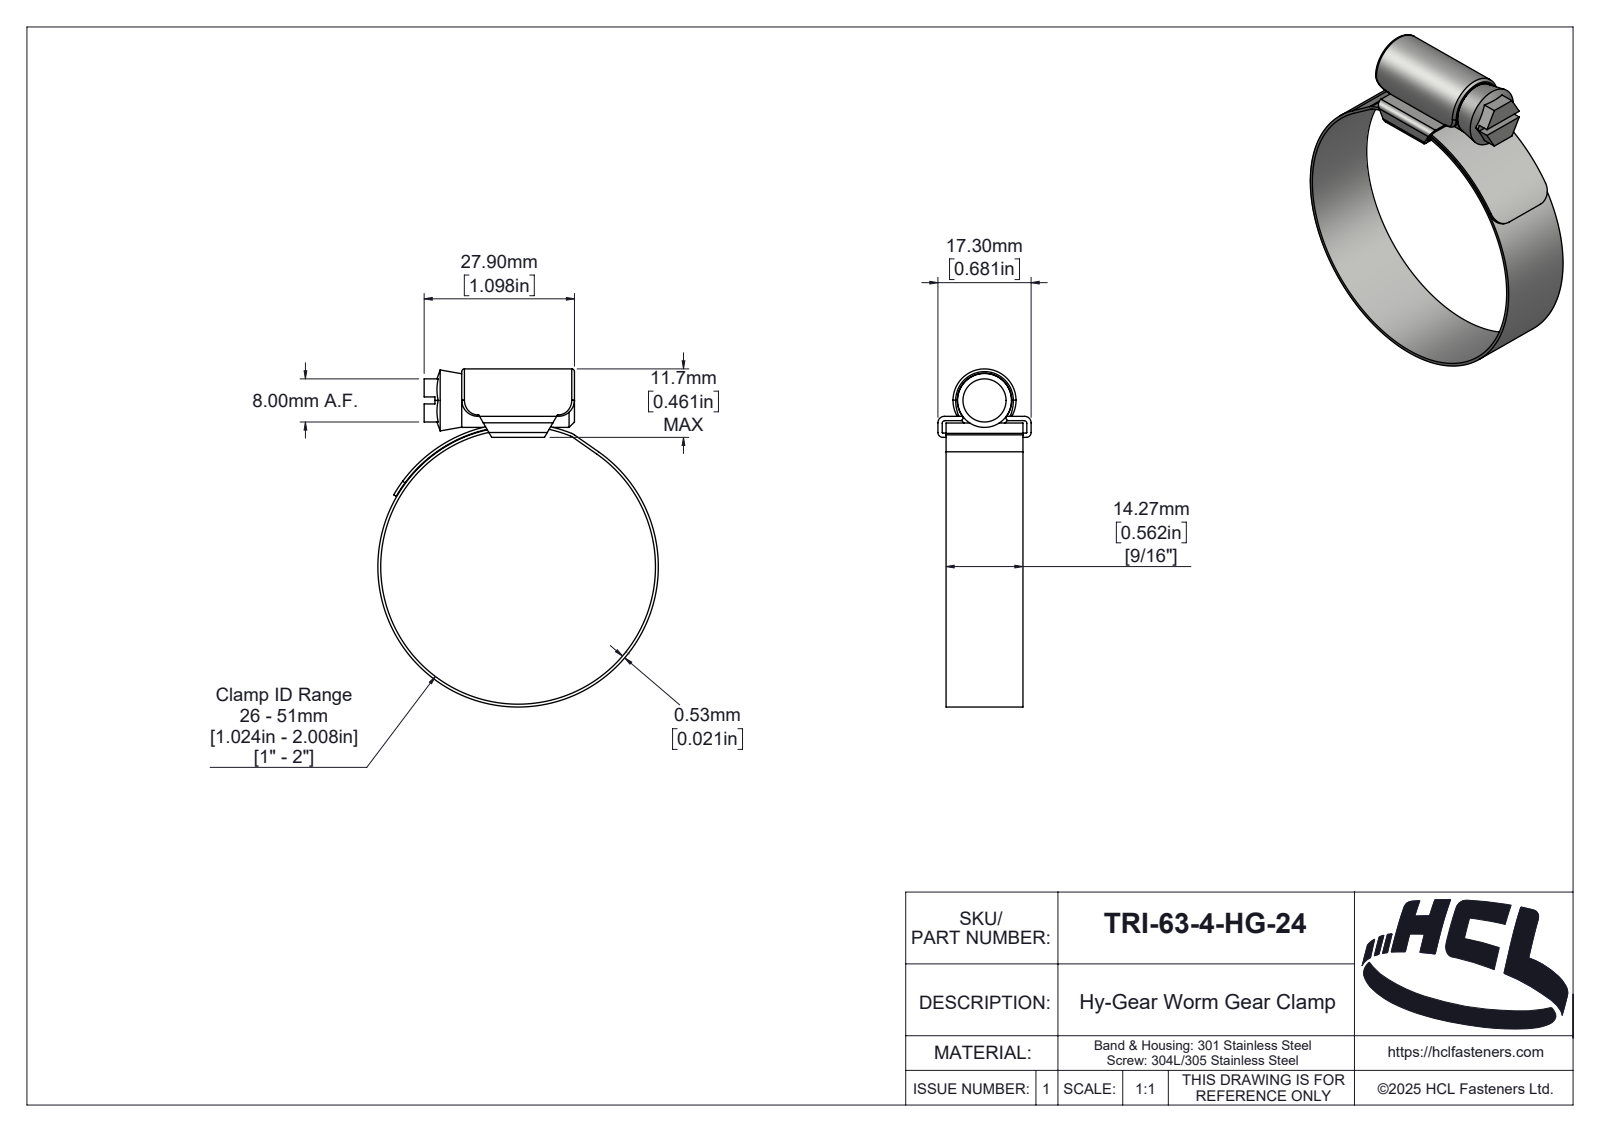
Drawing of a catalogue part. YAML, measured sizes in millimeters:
part_name: "TRI-50-0-HG-24"
step_written_by: "SolidWorks 2025 (AUTOMOTIVE_DESIGN)"
units: millimeters
bodies: {solids: 3, faces: 189, planar: 39, cylindrical: 89, other: 61}
overall_size: [62.73, 52.06, 17.3]
volume: 4226
surface_area: 8419
round_holes:
  - {diameter: 51, count: 1}
round_bosses_or_shafts:
  - {diameter: 52.06, count: 1}
  - {diameter: 10, count: 1}
partial_cylinders:
  - {radius: 0.5, count: 6}
  - {radius: 3, count: 4}
  - {radius: 0.1, count: 2}
  - {radius: 0.9, count: 2}
  - {radius: 1.2, count: 2}
  - {radius: 0.46, count: 1}
  - {radius: 1.89, count: 1}
  - {radius: 2, count: 1}
face_to_face_distances: [0.8, 3.1, 14.26, 2.3, 0.53, 3.9, 27.9, 1.52, 15.78, 16.5]
